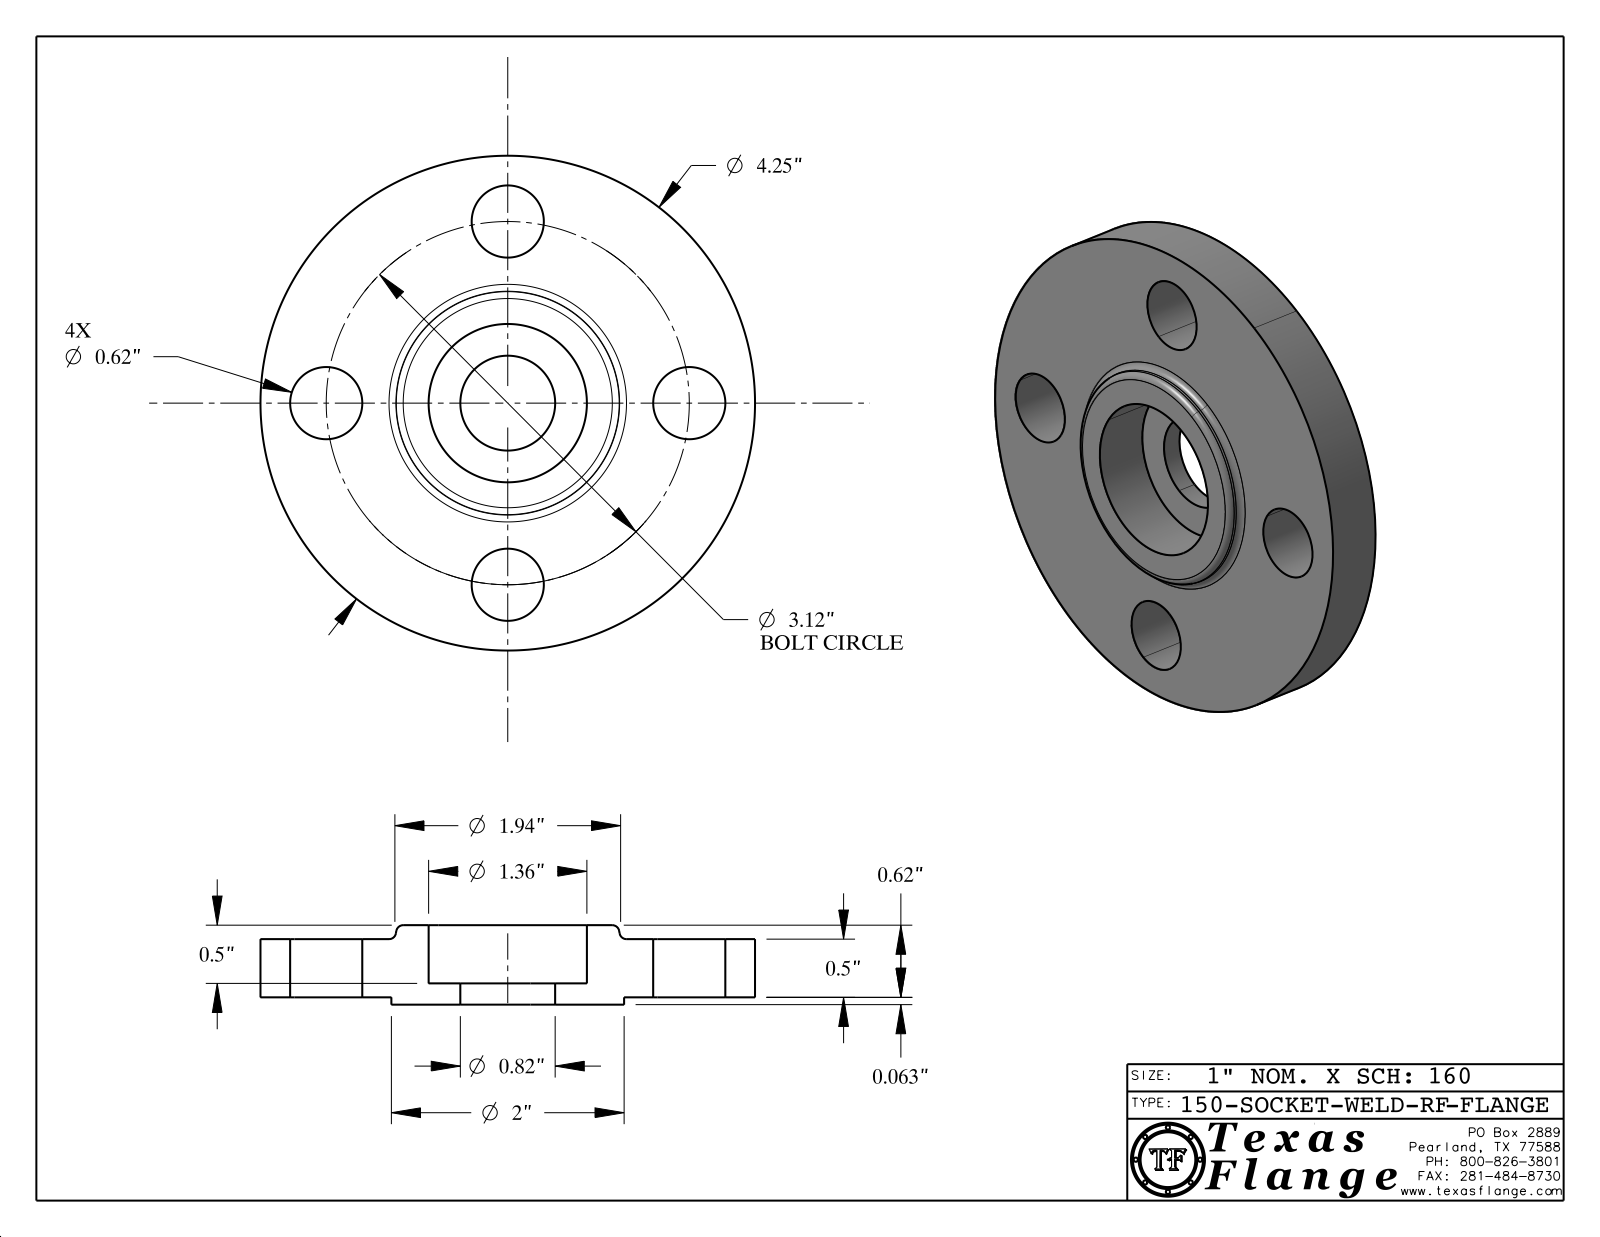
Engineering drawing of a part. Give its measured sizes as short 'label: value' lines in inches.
name: 150-SOCKET-WELD-RF
written by: CATIA V5 STEP AP214 (AUTOMOTIVE_DESIGN)
unit: in
bodies: 1 solid, 412 faces (370 planar, 36 cylindrical, 6 other)
size: 4.25 × 4.25 × 0.683
volume: 6.21 in³; area: 38.98 in²
holes: 4× ⌀0.62, 1× ⌀0.495, 1× ⌀0.815, 1× ⌀1.36
bosses: 8× ⌀0.03, 1× ⌀4.25, 1× ⌀2, 1× ⌀0.39
face distances: 0.5, 0.063, 0.563, 0.12, 0.683, 0.62, 0.183, 0.38, 0.548, 0.485
hole spacings: 1.56, 2.206, 1.194, 2.882, 3.12, 1.56
